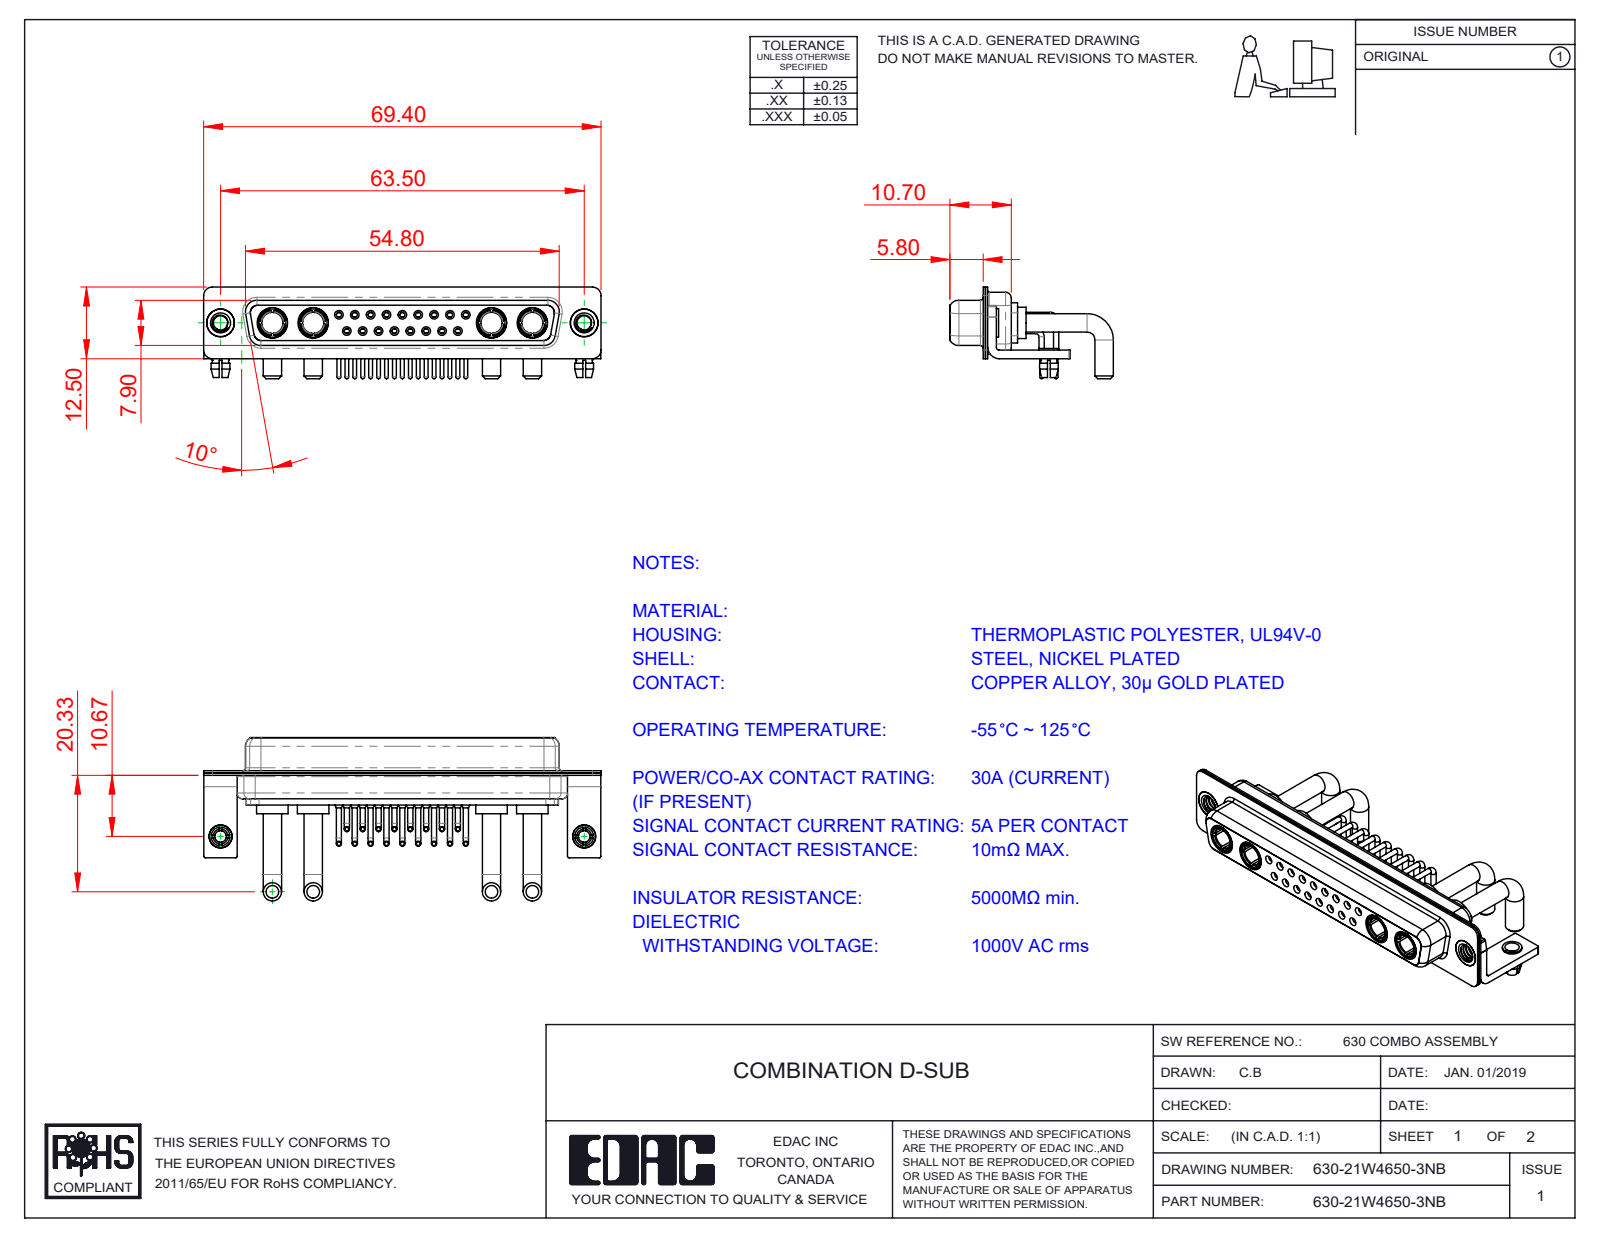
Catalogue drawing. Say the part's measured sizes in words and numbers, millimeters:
The part is named "630Combo Housing_21W4; 630-21W4650-3NB; 630Combo Contact Row 1; 630Combo Shell Front_37 Contacts (+6 more)". Its 3-D file was written by "SolidWorks 2020 (CONFIG_CONTROL_DESIGN)". It is 34 solids with 1622 faces: 506 planar, 678 cylindrical and 438 other. Overall it measures 69.4 by 28.53 by 16 millimeters. Its volume is 6 316 cubic millimeters and its surface area 13 716 square millimeters. Round holes: 19 of diameter 2, 17 of diameter 0.9, 17 of diameter 1.1, 17 of diameter 1.5, 9 of diameter 1.7, 8 of diameter 1.6, 6 of diameter 4.85, 4 of diameter 2.5, 4 of diameter 3.7, 4 of diameter 5.3, 2 of diameter 3.2, 2 of diameter 4. Round bosses or shafts: 23 of diameter 0.9, 17 of diameter 0.65, 15 of diameter 1.6, 8 of diameter 3.2, 6 of diameter 2, 6 of diameter 1.5, 4 of diameter 5.5, 4 of diameter 5.2. Partial cylindrical surfaces (rounded edges, fillets, slot ends): 16 of radius 0.25, 16 of radius 1.5, 13 of radius 2, 8 of radius 1.35, 8 of radius 1.6, 5 of radius 0.5, 4 of radius 0.6, 4 of radius 0.65. The main face-to-face distances are 0.4, 0.45, 1.4, 8.45, 1.8, 8.9, 6.2, 7.05, 0.8, 1.35. The hole center spacings are 3.16, 2.77, 5.54, 8.31, 5.03, 5.04, 7.49, 11.08.
